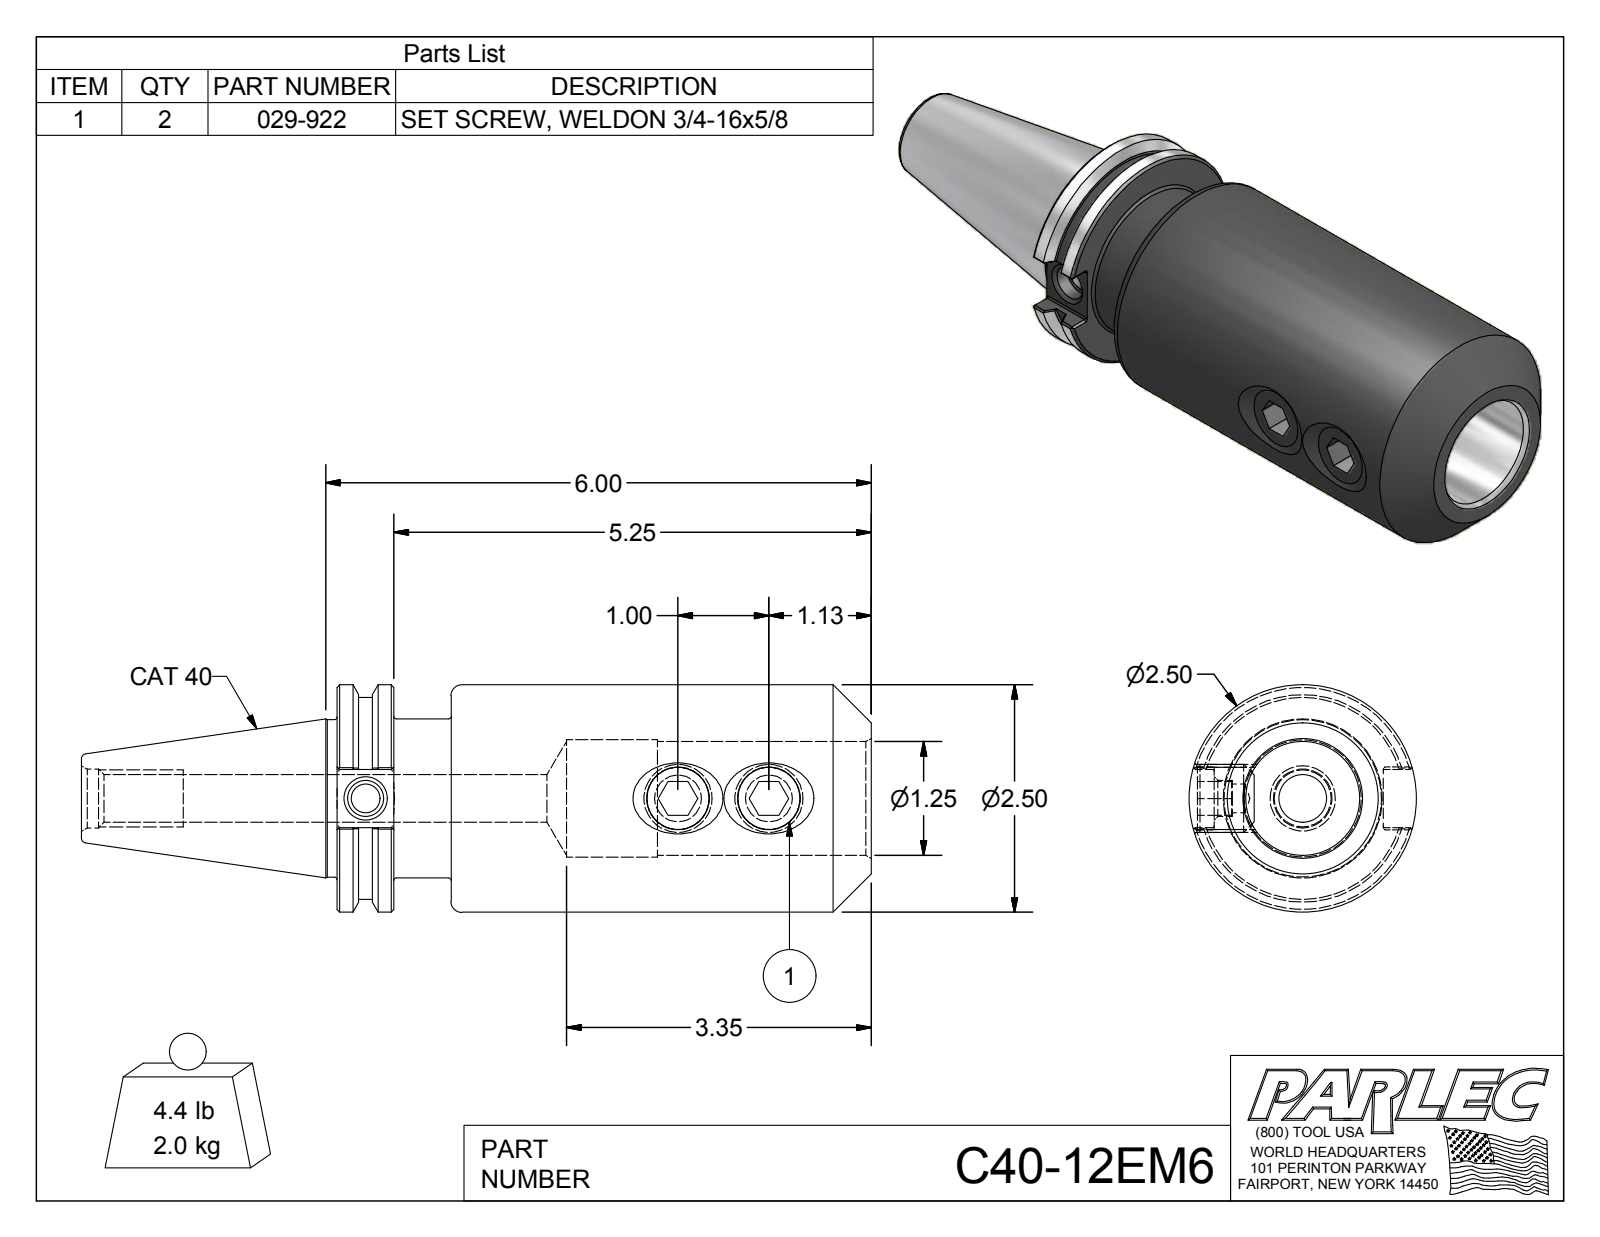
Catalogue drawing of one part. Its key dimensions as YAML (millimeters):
part_name: "C40-12EM6; C40-12EM6-1; 029-922"
step_written_by: "Autodesk Inventor 2012 (AUTOMOTIVE_DESIGN)"
units: millimeters
bodies: {solids: 3, faces: 119, planar: 52, cylindrical: 31, other: 36}
overall_size: [220.6, 63.5, 63.5]
volume: 408400
surface_area: 61880
round_holes:
  - {diameter: 17.3, count: 2}
  - {diameter: 8, count: 1}
  - {diameter: 10.1, count: 1}
  - {diameter: 13.4, count: 1}
  - {diameter: 16.5, count: 1}
  - {diameter: 31.8, count: 1}
  - {diameter: 32.8, count: 1}
round_bosses_or_shafts:
  - {diameter: 19.1, count: 2}
  - {diameter: 63.5, count: 1}
  - {diameter: 56.4, count: 1}
  - {diameter: 44.5, count: 1}
  - {diameter: 43.9, count: 1}
partial_cylinders:
  - {radius: 0.5, count: 12}
face_to_face_distances: [15.9, 31.9, 16, 149.2, 133.4, 117.3, 15.9, 9.5, 36.1, 52]
hole_center_spacings: [25.4, 87.2, 112.6]
